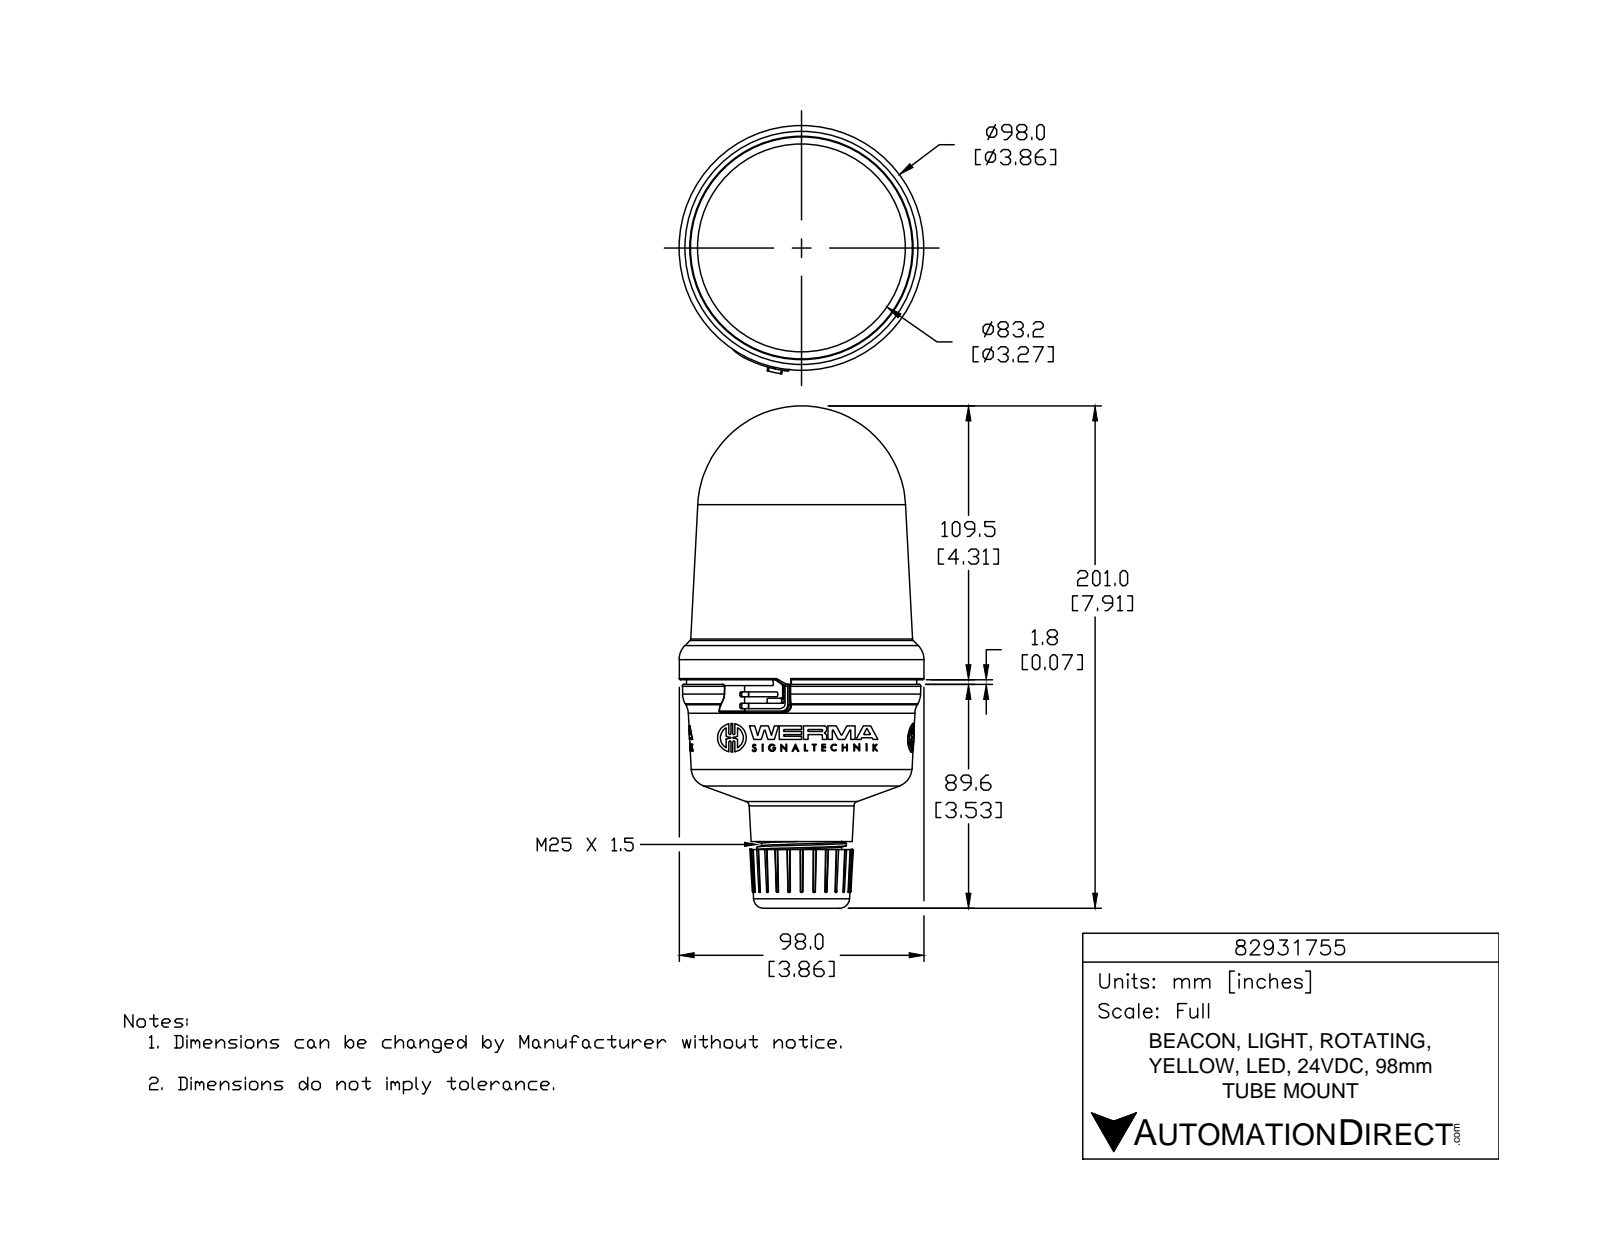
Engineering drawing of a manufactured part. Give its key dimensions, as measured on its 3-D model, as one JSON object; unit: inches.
{"part_name": "82931755", "step_written_by": "SolidWorks 2015 (AUTOMOTIVE_DESIGN)", "units": "inches", "bodies": {"solids": 1, "faces": 1006, "planar": 554, "cylindrical": 189, "other": 263}, "overall_size": [7.914, 3.912, 3.858], "volume_in3": 54.7, "surface_area_in2": 91.39, "round_holes": [[0.078, 3], [1.013, 1], [1.024, 1]], "round_bosses_or_shafts": [[0.452, 3], [0.113, 3], [3.858, 1], [1.409, 1], [1.261, 1]], "partial_cylinders_radius": [[0.02, 12], [0.007, 9], [0.007, 6], [0.016, 6], [0.016, 6], [0.016, 6], [0.262, 6], [0.006, 3]], "face_to_face_distances": [2.214, 0.462, 2.676, 0.335, 0.127, 2.548, 2.603, 2.476, 2.141, 0.073]}
